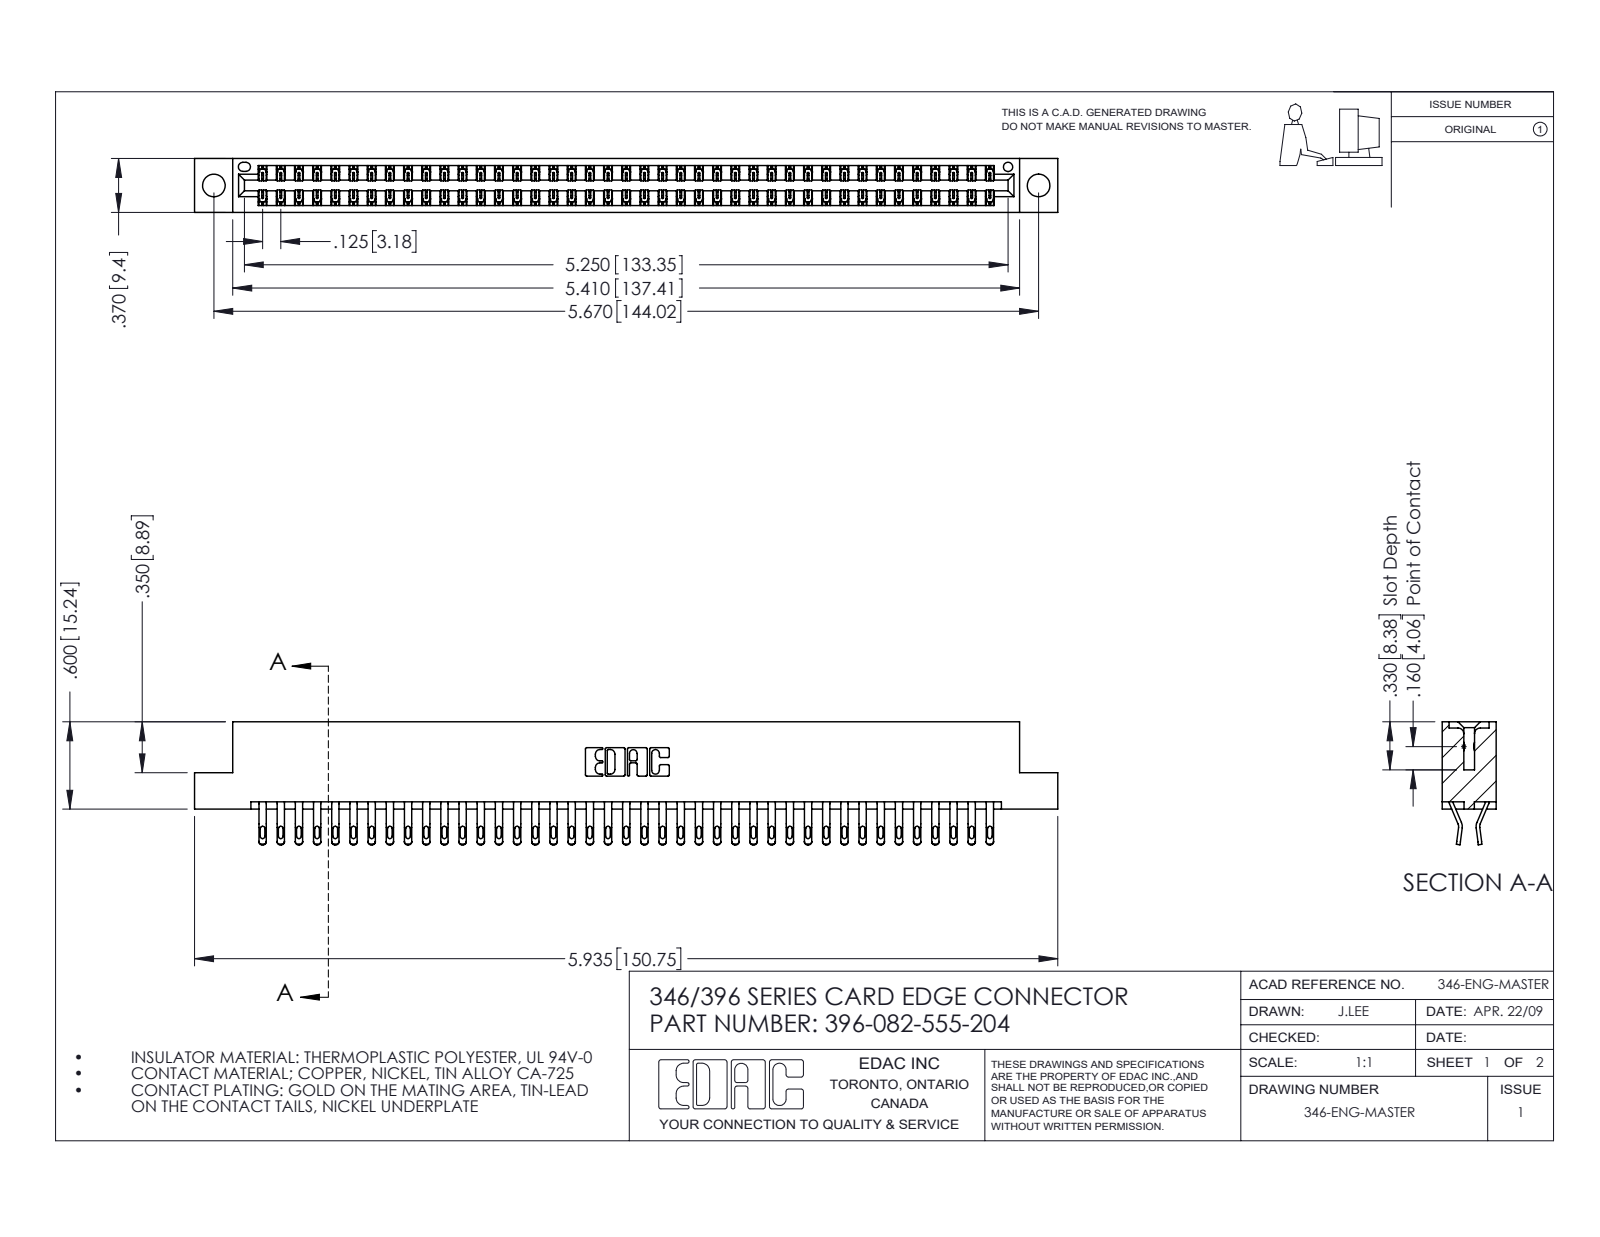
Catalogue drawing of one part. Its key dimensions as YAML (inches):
part_name: "396-082-555-204; 346 Part_Flush Mounting Lugs - 0.156 Dia-TH; 345-292-001_555 Tail"
step_written_by: "SolidWorks 2016 (CONFIG_CONTROL_DESIGN)"
units: inches
bodies: {solids: 83, faces: 4878, planar: 2782, cylindrical: 2096, other: 0}
overall_size: [5.935, 0.845, 0.37]
volume: 0.906
surface_area: 32.62
round_holes:
  - {diameter: 0.156, count: 2}
  - {diameter: 0.064, count: 1}
partial_cylinders:
  - {radius: 0.016, count: 164}
  - {radius: 0.02, count: 164}
  - {radius: 0.006, count: 123}
  - {radius: 0.01, count: 22}
  - {radius: 0.007, count: 6}
  - {radius: 0.031, count: 6}
  - {radius: 0.026, count: 3}
  - {radius: 0.01, count: 2}
face_to_face_distances: [0.048, 0.322, 0.37, 0.25, 0.025, 0.072, 0.298, 0.275, 0.148, 0.222]
hole_center_spacings: [0.246, 5.461, 5.67]
